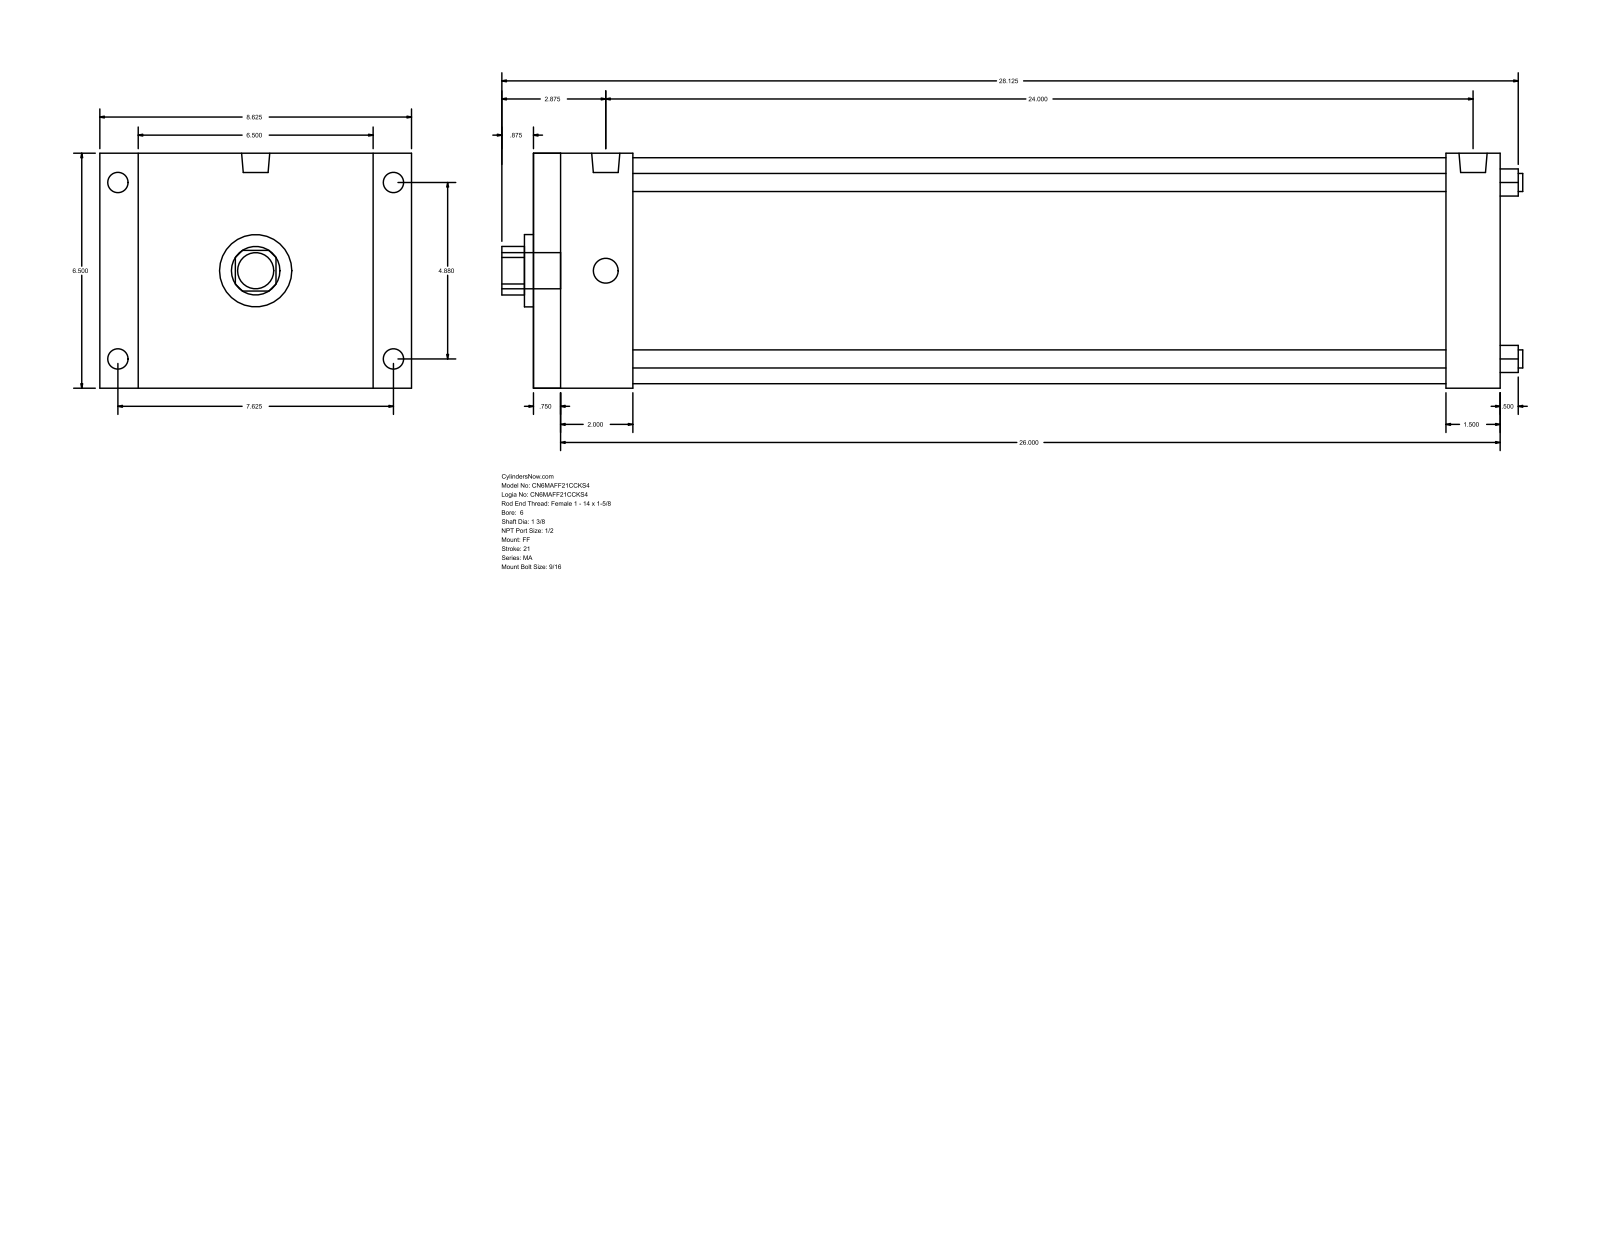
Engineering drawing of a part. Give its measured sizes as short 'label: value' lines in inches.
name: MA_FF__0600_1.375
written by: GSSL Pune (CONFIG_CONTROL_DESIGN)
unit: in
bodies: 0 solids, 92 faces (64 planar, 28 cylindrical, 0 other)
size: 28.25 × 8.625 × 6.5
holes: 4× ⌀0.5, 1× ⌀1.375, 1× ⌀2, 1× ⌀6.25
bosses: 4× ⌀0.687, 4× ⌀0.563, 2× ⌀0.778, 1× ⌀1
rounds: 1× R0.672
face distances: 6.5, 26.75, 0.625, 26.125, 2, 24.625, 2.625, 24.125, 25.25, 22.625
hole spacings: 3.451, 4.88, 6.902
